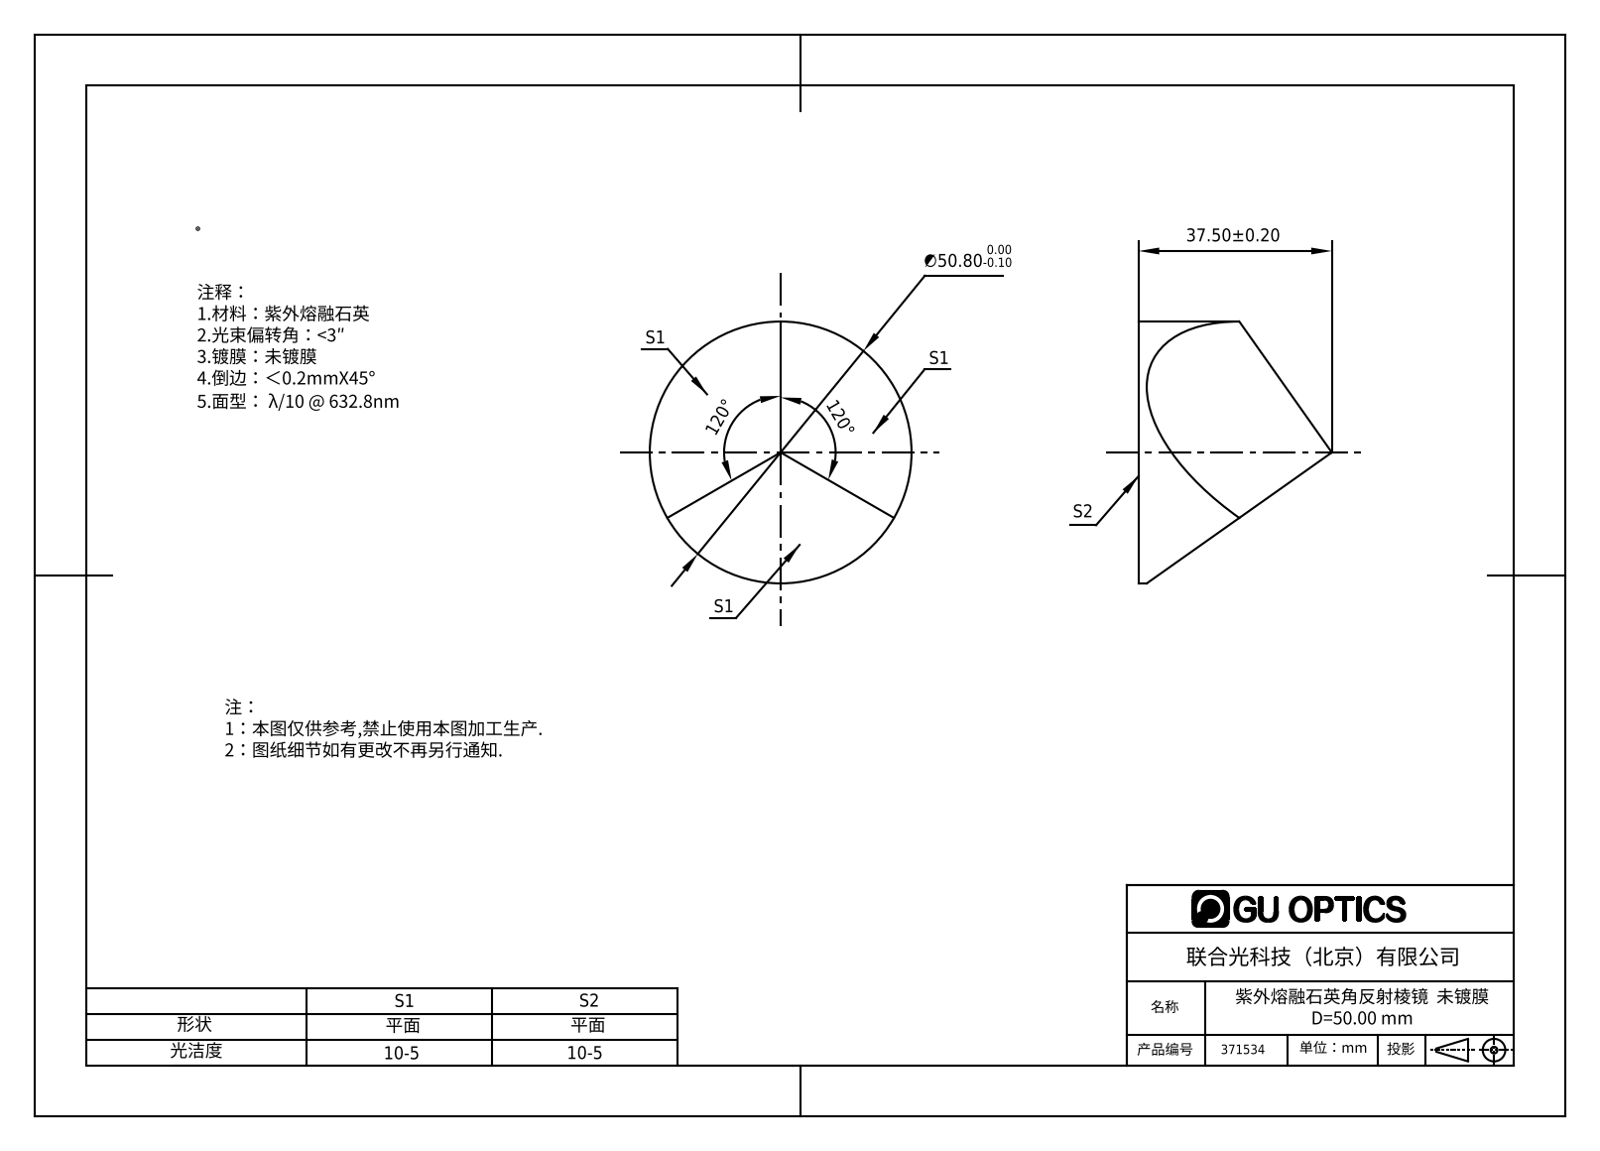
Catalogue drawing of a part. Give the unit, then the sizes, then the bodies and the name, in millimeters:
Units: millimetres
Overall size (bounding box): 50.8 × 50.8 × 37.5
Round bosses / shafts (diameter × count): ⌀50.8 ×1
Volume: 35 875 mm³ · Surface area: 6 782 mm²
Bodies: 1 solid, 6 faces (4 planar, 2 cylindrical, 0 other)
Part name (STEP PRODUCT): 371507
STEP written by: SolidWorks 2016 (CONFIG_CONTROL_DESIGN)
